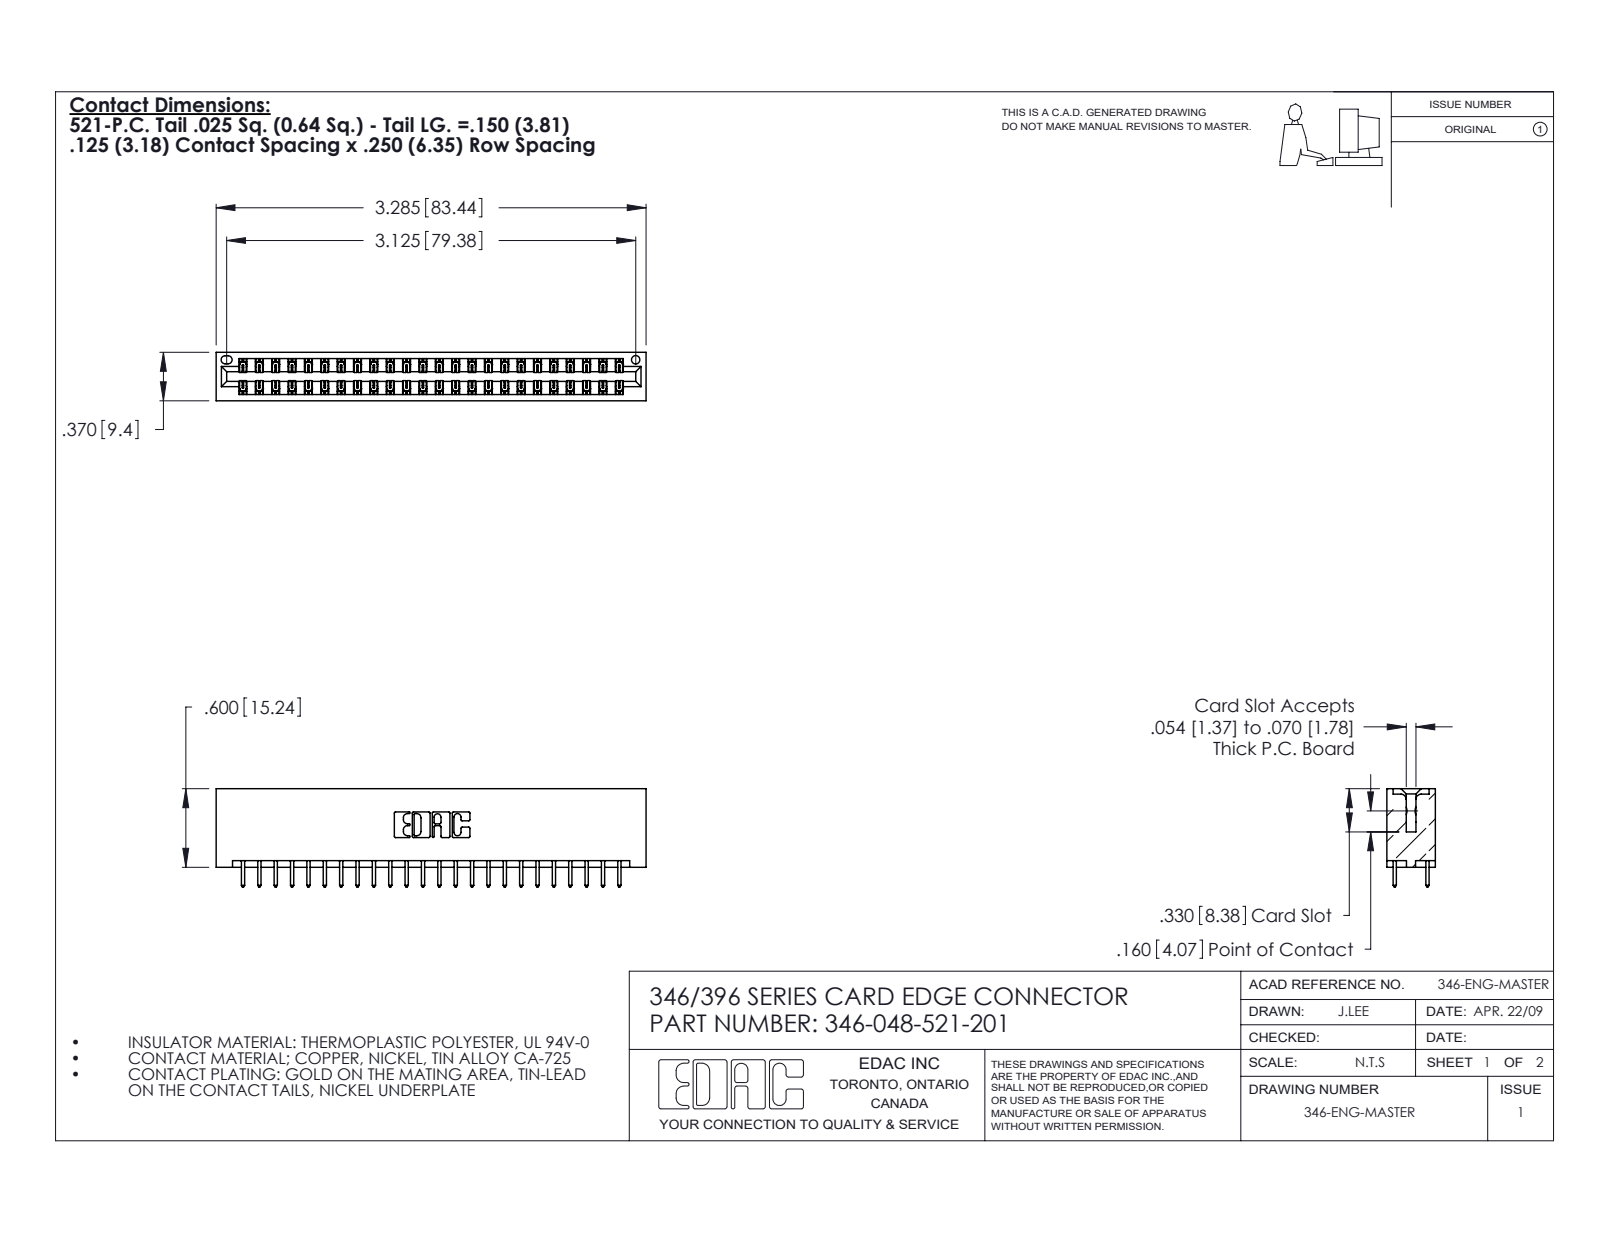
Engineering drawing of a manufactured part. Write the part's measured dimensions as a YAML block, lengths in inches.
part_name: "346-048-521-201; 345-292-001_345-293-121; 346 Part_No Mounting Lugs"
step_written_by: "SolidWorks 2020 (CONFIG_CONTROL_DESIGN)"
units: inches
bodies: {solids: 49, faces: 2610, planar: 1752, cylindrical: 858, other: 0}
overall_size: [3.285, 0.75, 0.37]
volume: 0.522
surface_area: 17.83
round_holes:
  - {diameter: 0.064, count: 1}
partial_cylinders:
  - {radius: 0.006, count: 72}
  - {radius: 0.01, count: 48}
  - {radius: 0.01, count: 22}
  - {radius: 0.007, count: 6}
  - {radius: 0.031, count: 6}
  - {radius: 0.026, count: 3}
  - {radius: 0.014, count: 2}
  - {radius: 0.022, count: 2}
face_to_face_distances: [0.048, 0.322, 0.25, 0.37, 0.072, 0.298, 0.025, 0.275, 0.148, 0.222]
